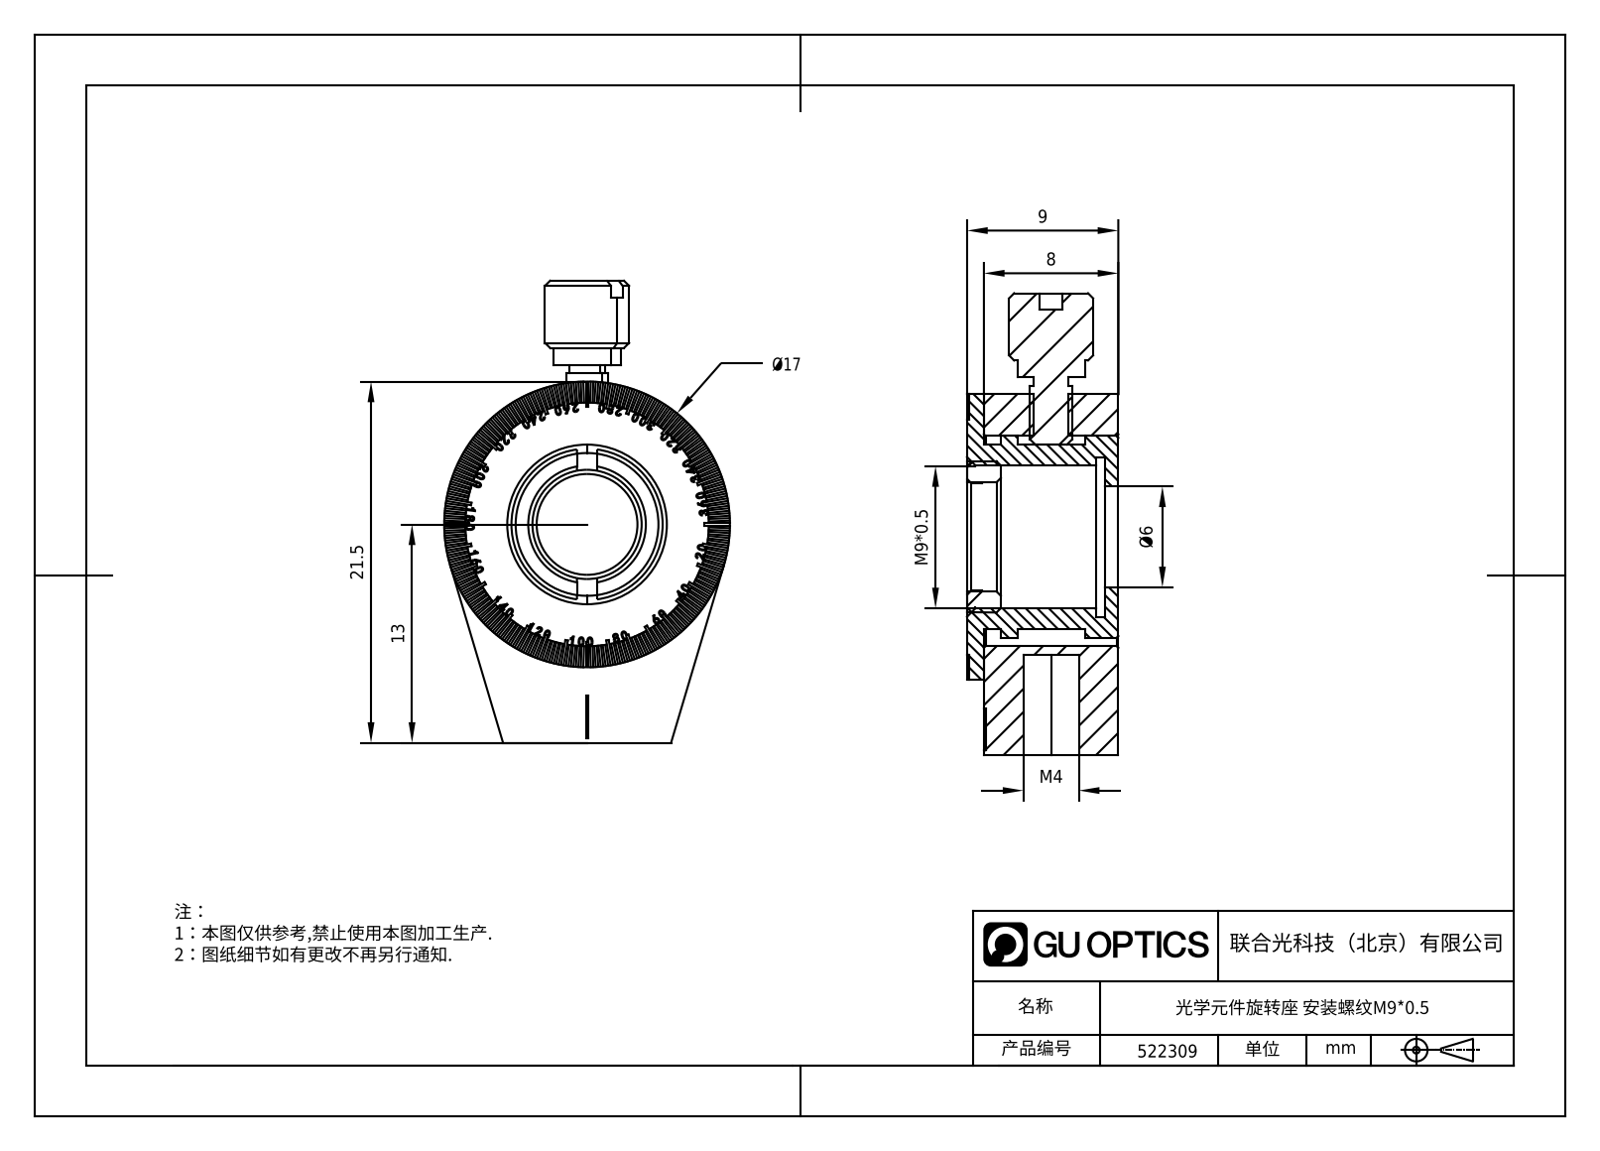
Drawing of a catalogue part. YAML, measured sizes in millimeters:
part_name: "一体式手拧螺丝_M2.5X4; ZFK透镜卡环压圈_1.8.5.9-ZFK-K8"
step_written_by: "SolidWorks 2021 (CONFIG_CONTROL_DESIGN)"
units: millimeters
bodies: {solids: 4, faces: 1248, planar: 992, cylindrical: 37, other: 219}
overall_size: [27.5, 17, 9]
volume: 2054
surface_area: 2651
round_holes:
  - {diameter: 2.05, count: 1}
  - {diameter: 3.3, count: 1}
  - {diameter: 6, count: 1}
  - {diameter: 6.5, count: 1}
  - {diameter: 8.5, count: 1}
  - {diameter: 9.5, count: 1}
round_bosses_or_shafts:
  - {diameter: 17, count: 1}
  - {diameter: 12, count: 1}
  - {diameter: 11, count: 1}
  - {diameter: 9, count: 1}
  - {diameter: 5, count: 1}
  - {diameter: 4, count: 1}
  - {diameter: 2.5, count: 1}
  - {diameter: 2.1, count: 1}
partial_cylinders:
  - {radius: 5, count: 1}
face_to_face_distances: [8, 1, 9, 2, 7, 0.8, 6, 7.2, 8.2, 0.9]
